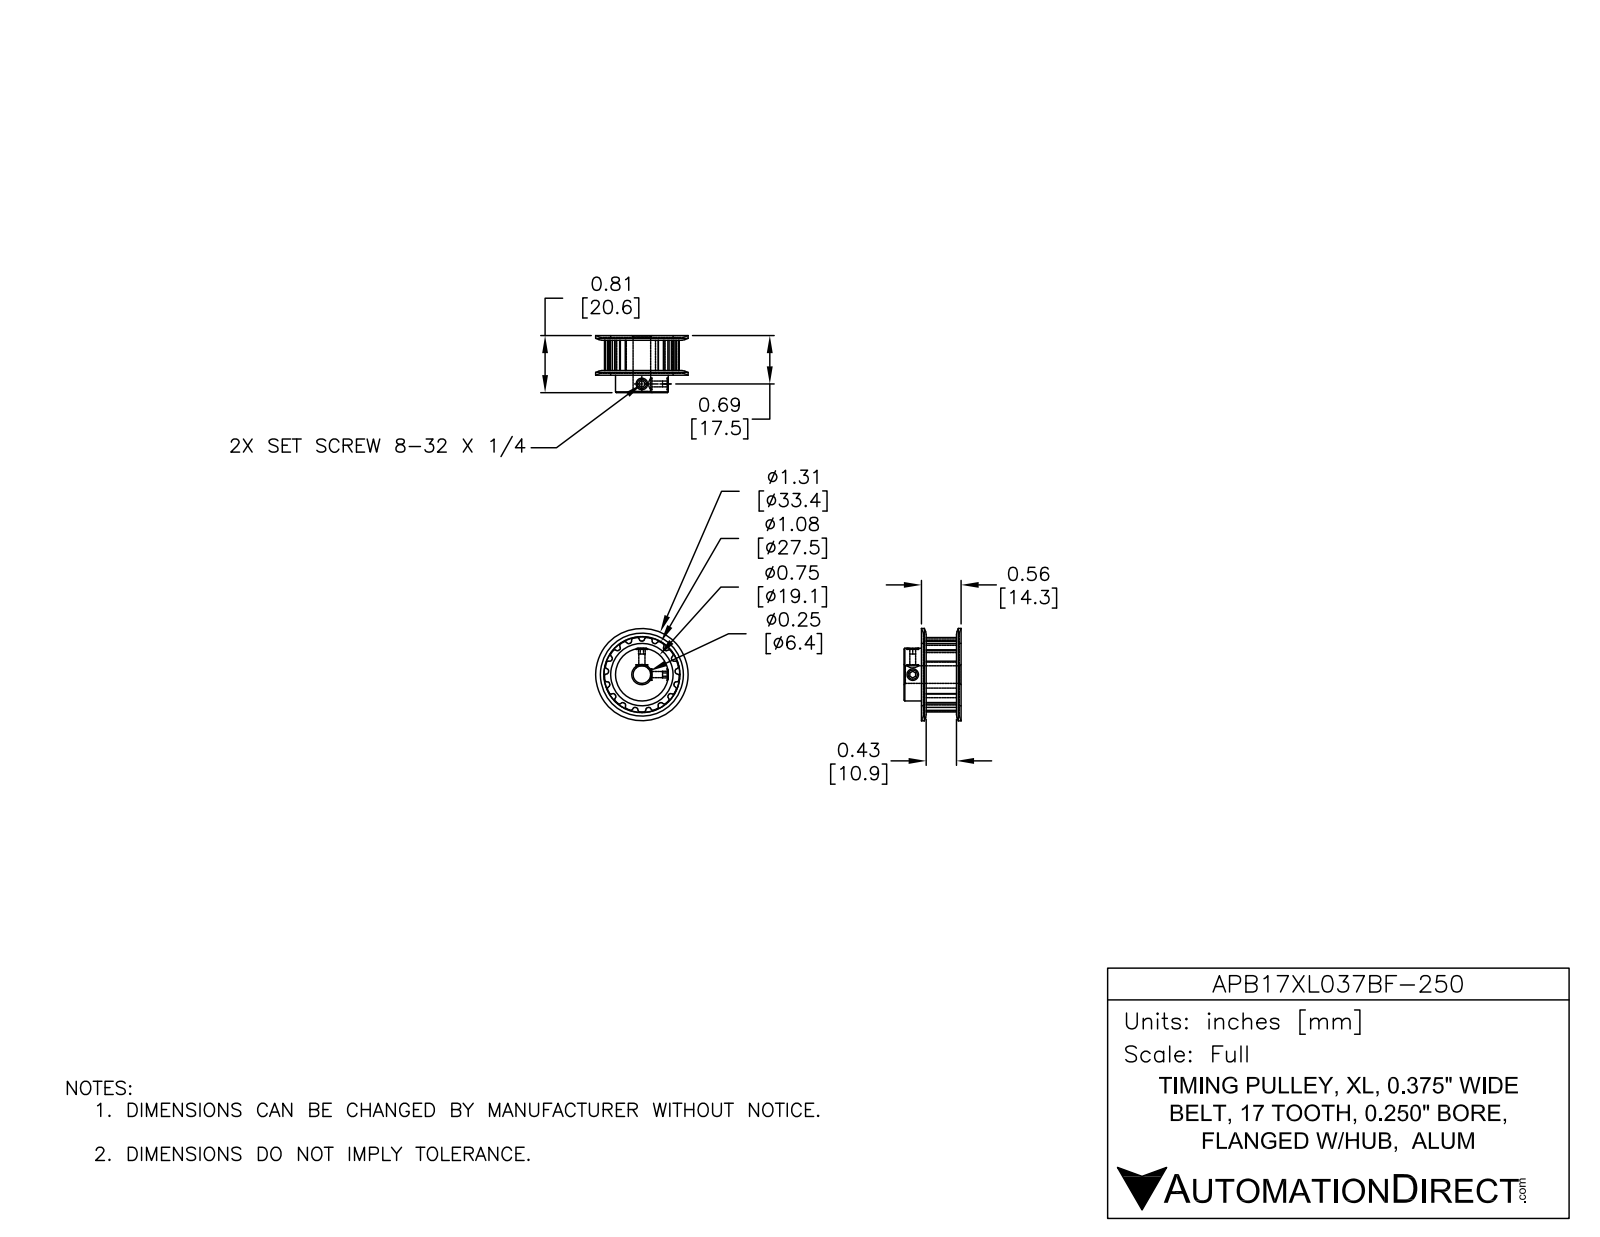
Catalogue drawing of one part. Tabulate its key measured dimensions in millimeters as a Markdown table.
| quantity | value |
| --- | --- |
| part name | APB17XL037BF-250 |
| STEP written by | SolidWorks 2014 (AUTOMOTIVE_DESIGN) |
| units | millimeters |
| bodies | 1 solid, 189 faces (57 planar, 110 cylindrical, 22 other) |
| overall size | 33.4 × 33.4 × 20.7 |
| volume | 8 780 mm³ |
| surface area | 4 692 mm² |
| round holes (diameter × count) | 2.2 × 2, 6.4 × 1 |
| round bosses / shafts (diameter × count) | 19.1 × 1 |
| partial cylindrical surfaces (radius × count) | 0.4 × 68, 12.1 × 1 |
| main face-to-face distances | 12.6, 0.8, 13.4, 20.7, 19.8, 7.2, 11.7, 8.1, 1.7, 0.8 |
